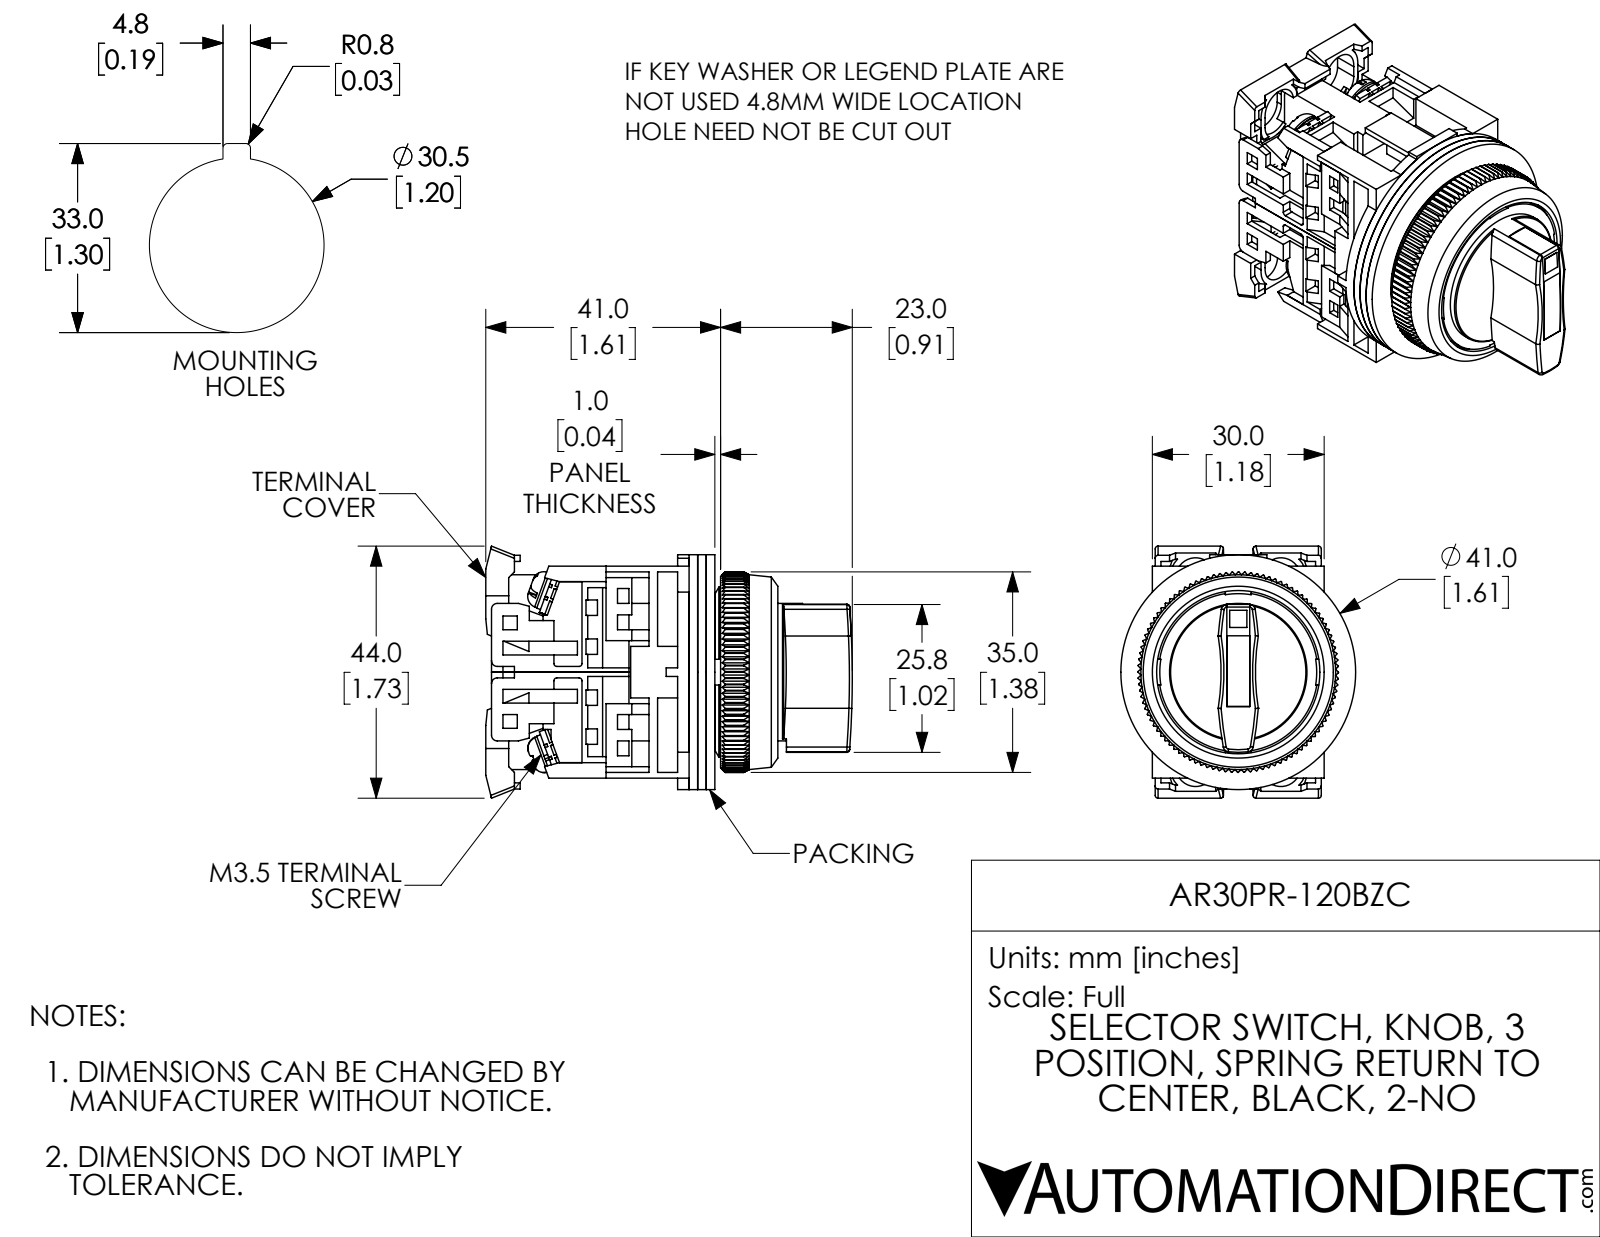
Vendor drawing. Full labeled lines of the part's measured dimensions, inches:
Part name (STEP PRODUCT): AR30PR-120BZC
STEP written by: SolidWorks 2017 (AUTOMOTIVE_DESIGN)
Units: inches
Bodies: 26 solids, 1771 faces (1219 planar, 324 cylindrical, 228 other)
Overall size (bounding box): 2.52 × 1.732 × 1.614
Volume: 2.318 in³ · Surface area: 62.54 in²
Round holes (diameter × count): ⌀0.138 ×8, ⌀0.142 ×4, ⌀0.118 ×1, ⌀0.315 ×1, ⌀0.472 ×1, ⌀0.48 ×1, ⌀0.512 ×1, ⌀0.819 ×1, ⌀0.945 ×1, ⌀1.122 ×1, ⌀1.252 ×1
Round bosses / shafts (diameter × count): ⌀0.26 ×4, ⌀0.138 ×4, ⌀1.614 ×1, ⌀1.181 ×1, ⌀0.787 ×1, ⌀0.709 ×1, ⌀0.669 ×1, ⌀0.559 ×1
Partial cylindrical surfaces — rounded edges, fillets, slot ends (radius × count): R0.059 ×16, R0.02 ×13, R0.039 ×8, R0.138 ×4, R0.177 ×4, R0.118 ×2, R1.575 ×2, R1.638 ×2
Main face-to-face distances: 0.059, 0.118, 0.039, 0.177, 1.417, 0.079, 1.358, 0.689, 0.091, 0.157
Hole centre spacings: 0.579, 0.61
